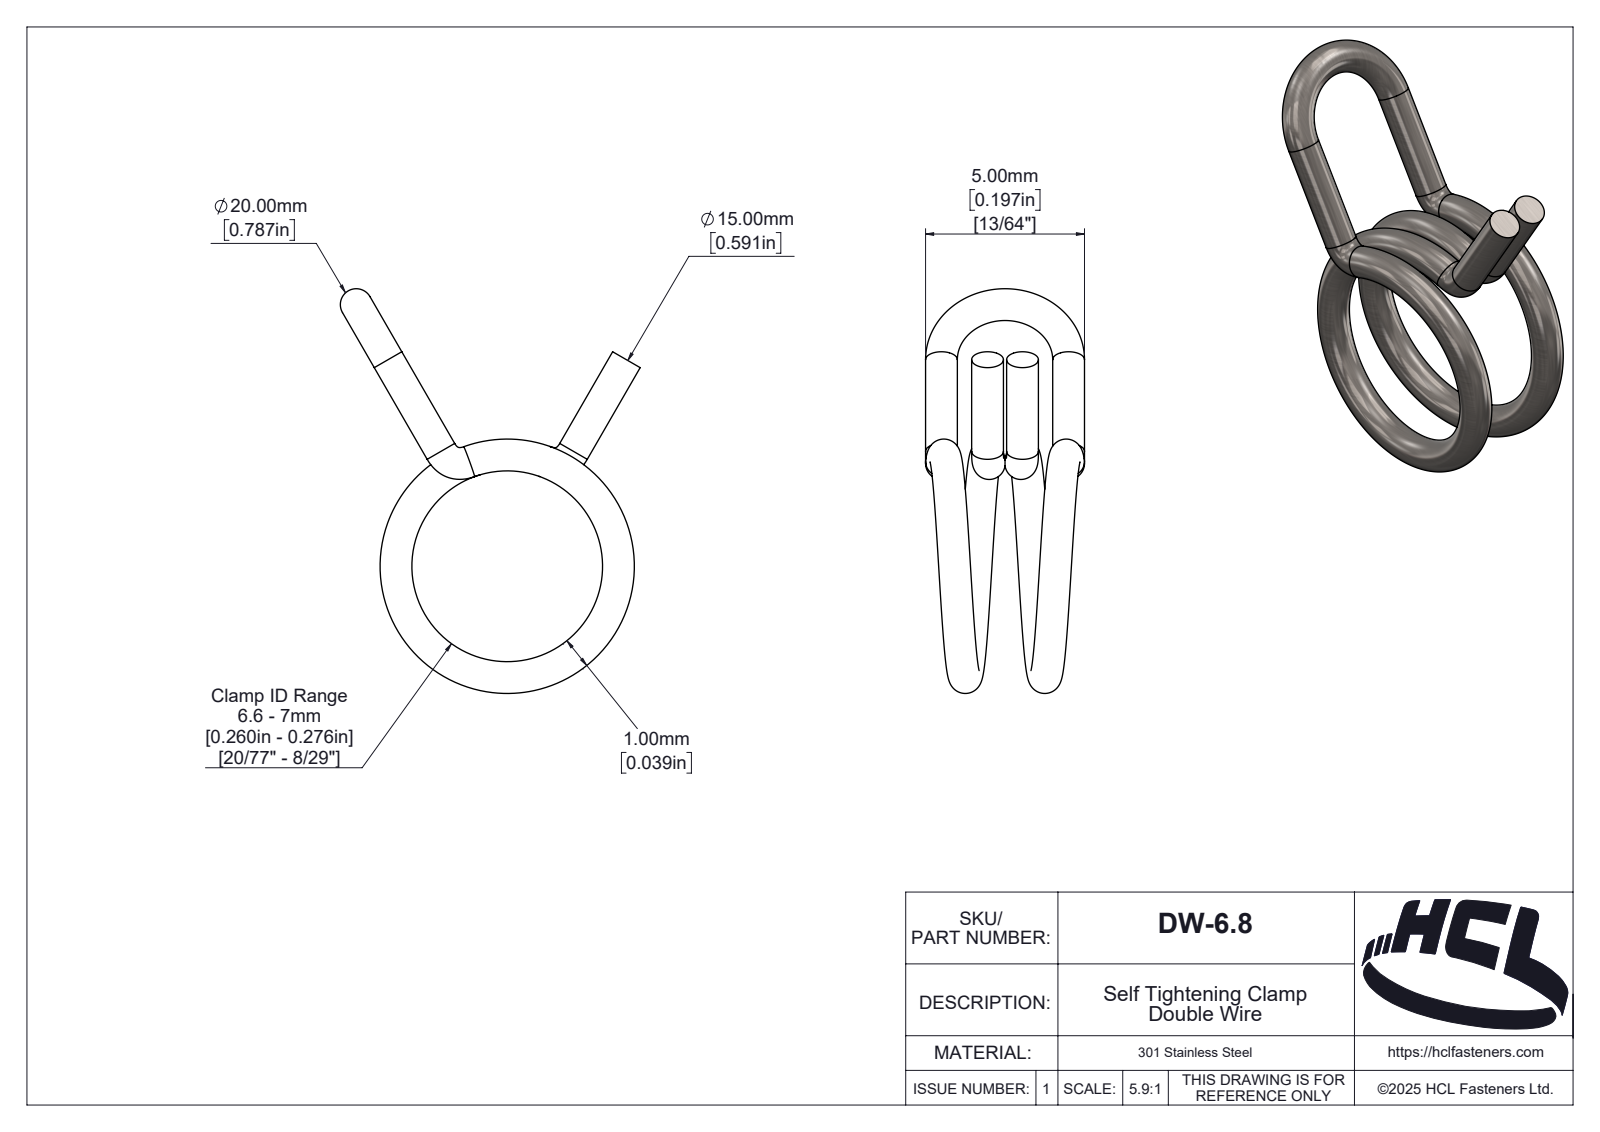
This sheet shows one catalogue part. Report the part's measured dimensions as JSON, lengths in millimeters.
{"part_name": "DW-6.8", "step_written_by": "SolidWorks 2025 (AUTOMOTIVE_DESIGN)", "units": "millimeters", "bodies": {"solids": 1, "faces": 125, "planar": 14, "cylindrical": 53, "other": 58}, "overall_size": [12.73, 9.43, 5], "volume_mm3": 57, "surface_area_mm2": 230, "round_bosses_or_shafts": [[1, 4]], "partial_cylinders_radius": [[0.16, 1], [0.2, 1], [0.21, 1], [0.26, 1], [0.36, 1], [0.48, 1], [0.6, 1], [0.68, 1]]}
